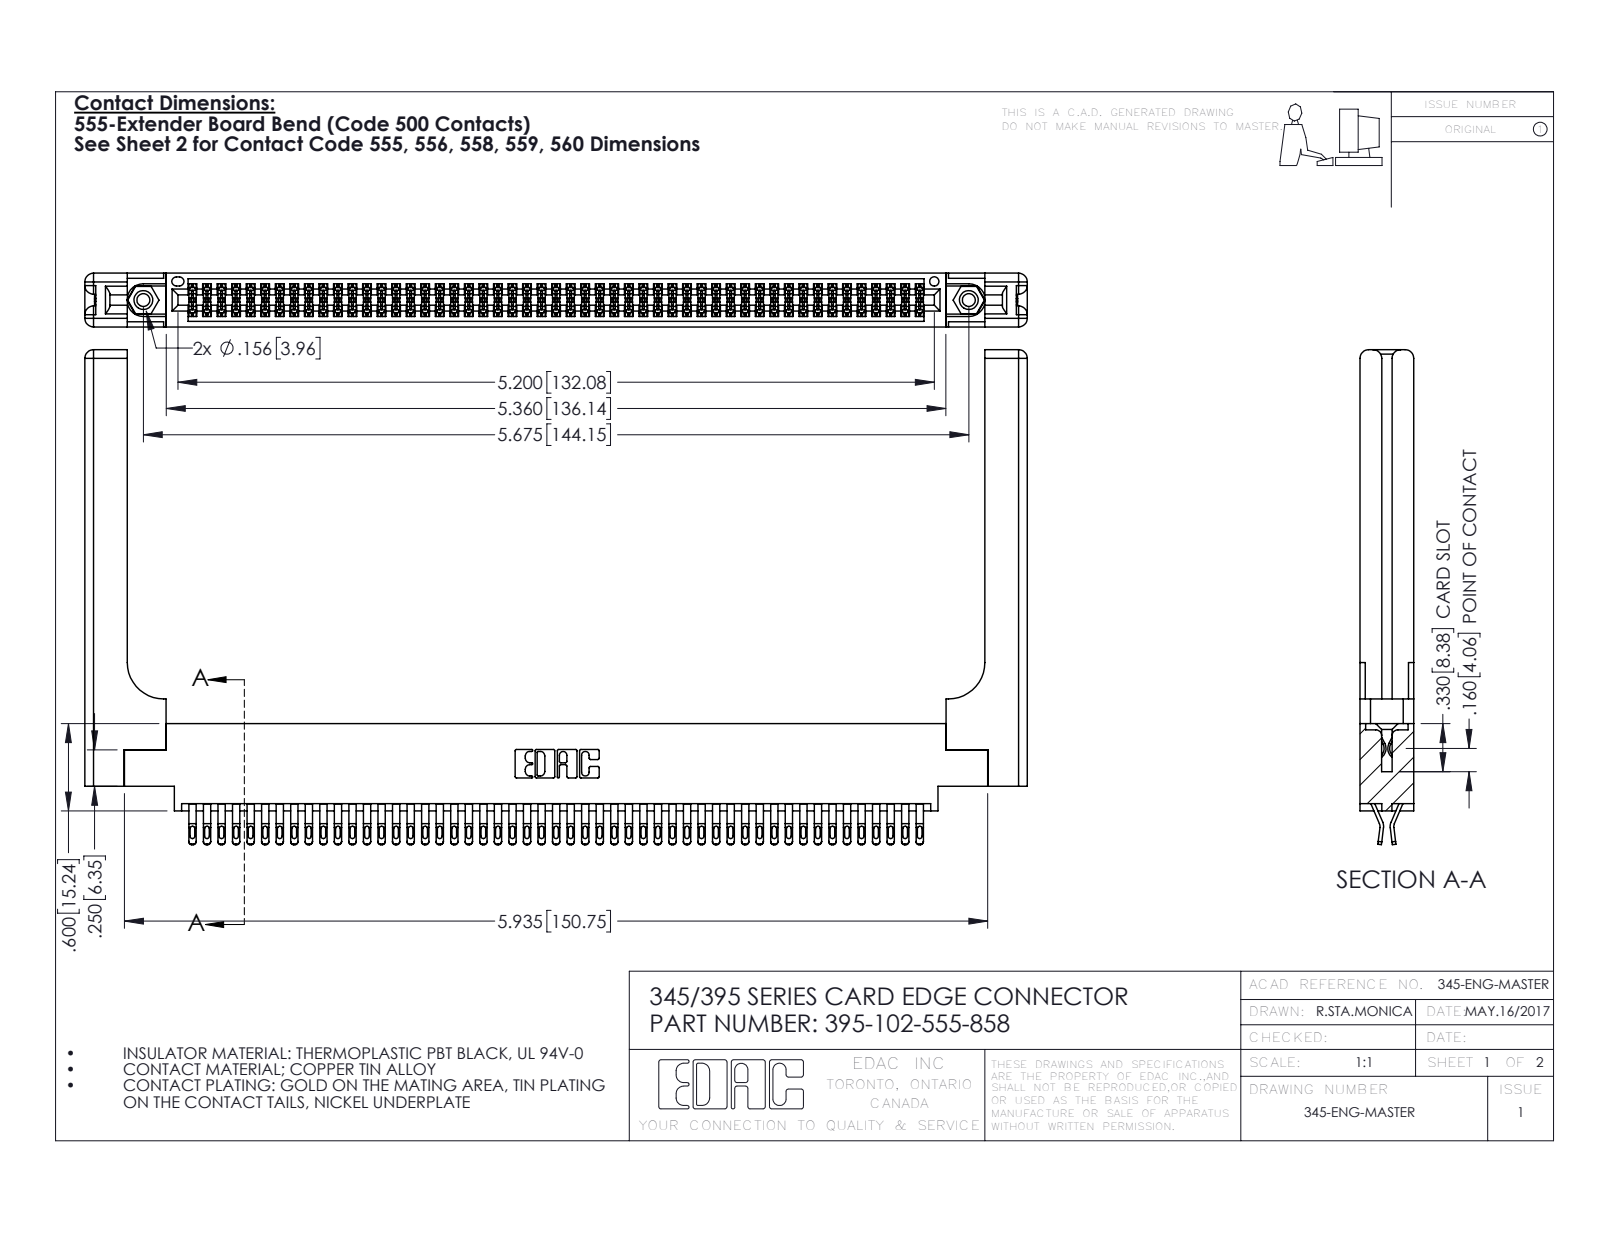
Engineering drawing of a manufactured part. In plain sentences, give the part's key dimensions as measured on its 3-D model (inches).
The part is named "345-292-001_555 Tail; 395-102-555-858; 345 Part_0.170 Offset - 0.156 Dia-TH; 345-250-001_345-250-001-102 (+1 more)". Its 3-D file was written by "SolidWorks 2016 (CONFIG_CONTROL_DESIGN)". It is 107 solids with 6098 faces: 3394 planar, 2644 cylindrical and 60 other. Overall it measures 6.479 by 3.402 by 0.37 inches. Its volume is 1.509 cubic inches and its surface area 47.17 square inches. Round holes: 2 of diameter 0.089, 2 of diameter 0.125, 2 of diameter 0.156, 1 of diameter 0.064. Round bosses or shafts: 2 of diameter 0.155. Partial cylindrical surfaces (rounded edges, fillets, slot ends): 255 of radius 0.016, 204 of radius 0.02, 153 of radius 0.006, 22 of radius 0.01, 16 of radius 0.06, 6 of radius 0.007, 6 of radius 0.031, 3 of radius 0.026. The main face-to-face distances are 0.072, 0.37, 0.298, 0.025, 0.098, 0.272, 0.2, 0.225, 0.175, 0.148. The hole center spacings are 0.27, 5.439, 5.675.
